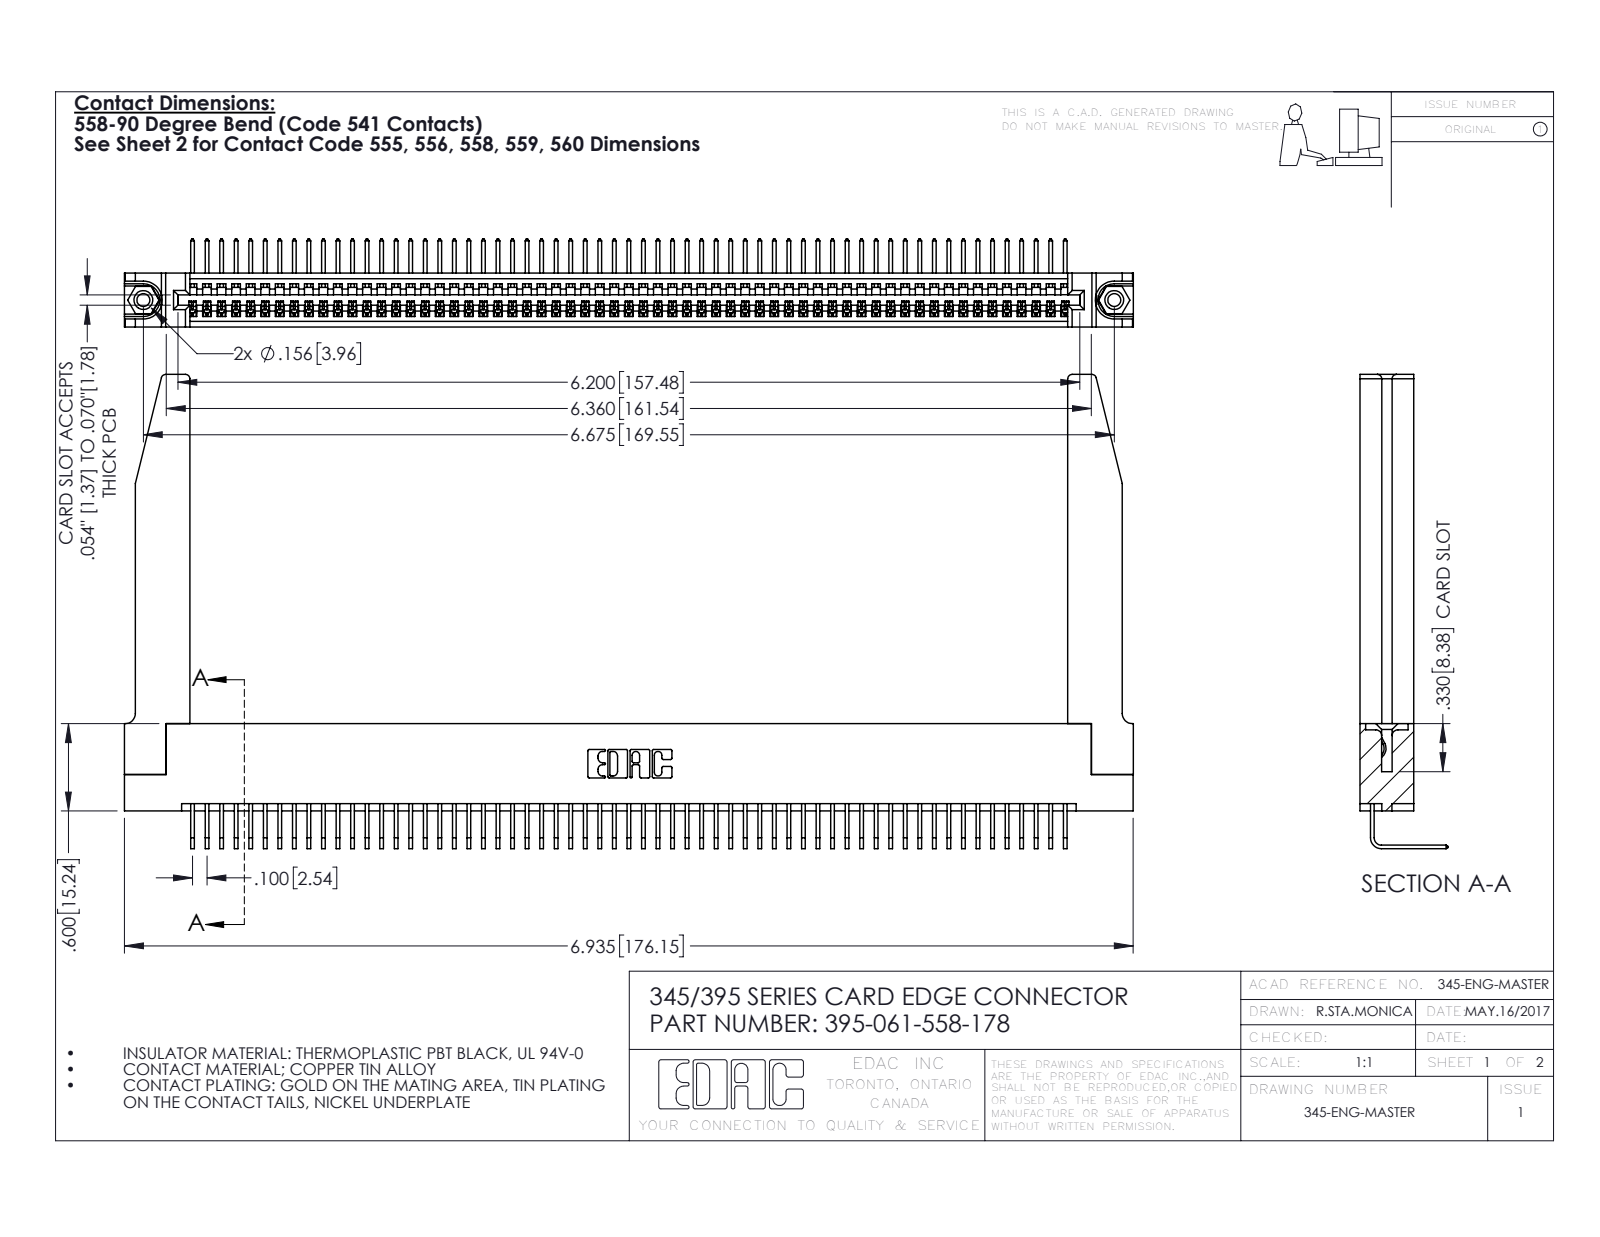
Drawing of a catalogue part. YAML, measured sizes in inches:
part_name: "395-061-558-178; 345 Part_Flush Mounting Lugs - 0.156 Dia-TH; 345-292-001_558 Tail - 2; 345-220-078_345-220-078 (+1 more)"
step_written_by: "SolidWorks 2016 (CONFIG_CONTROL_DESIGN)"
units: inches
bodies: {solids: 66, faces: 4020, planar: 2784, cylindrical: 1184, other: 52}
overall_size: [6.936, 3.259, 0.605]
volume: 1.517
surface_area: 48.07
round_holes:
  - {diameter: 0.089, count: 2}
  - {diameter: 0.125, count: 2}
  - {diameter: 0.156, count: 2}
  - {diameter: 0.064, count: 1}
round_bosses_or_shafts:
  - {diameter: 0.155, count: 2}
partial_cylinders:
  - {radius: 0.006, count: 122}
  - {radius: 0.01, count: 22}
  - {radius: 0.03, count: 8}
  - {radius: 0.007, count: 6}
  - {radius: 0.031, count: 6}
  - {radius: 0.026, count: 3}
  - {radius: 0.031, count: 2}
  - {radius: 0.04, count: 2}
face_to_face_distances: [0.072, 0.37, 0.298, 0.2, 0.098, 0.272, 0.025, 0.225, 0.148, 0.15]
hole_center_spacings: [0.27, 6.439, 6.675]
